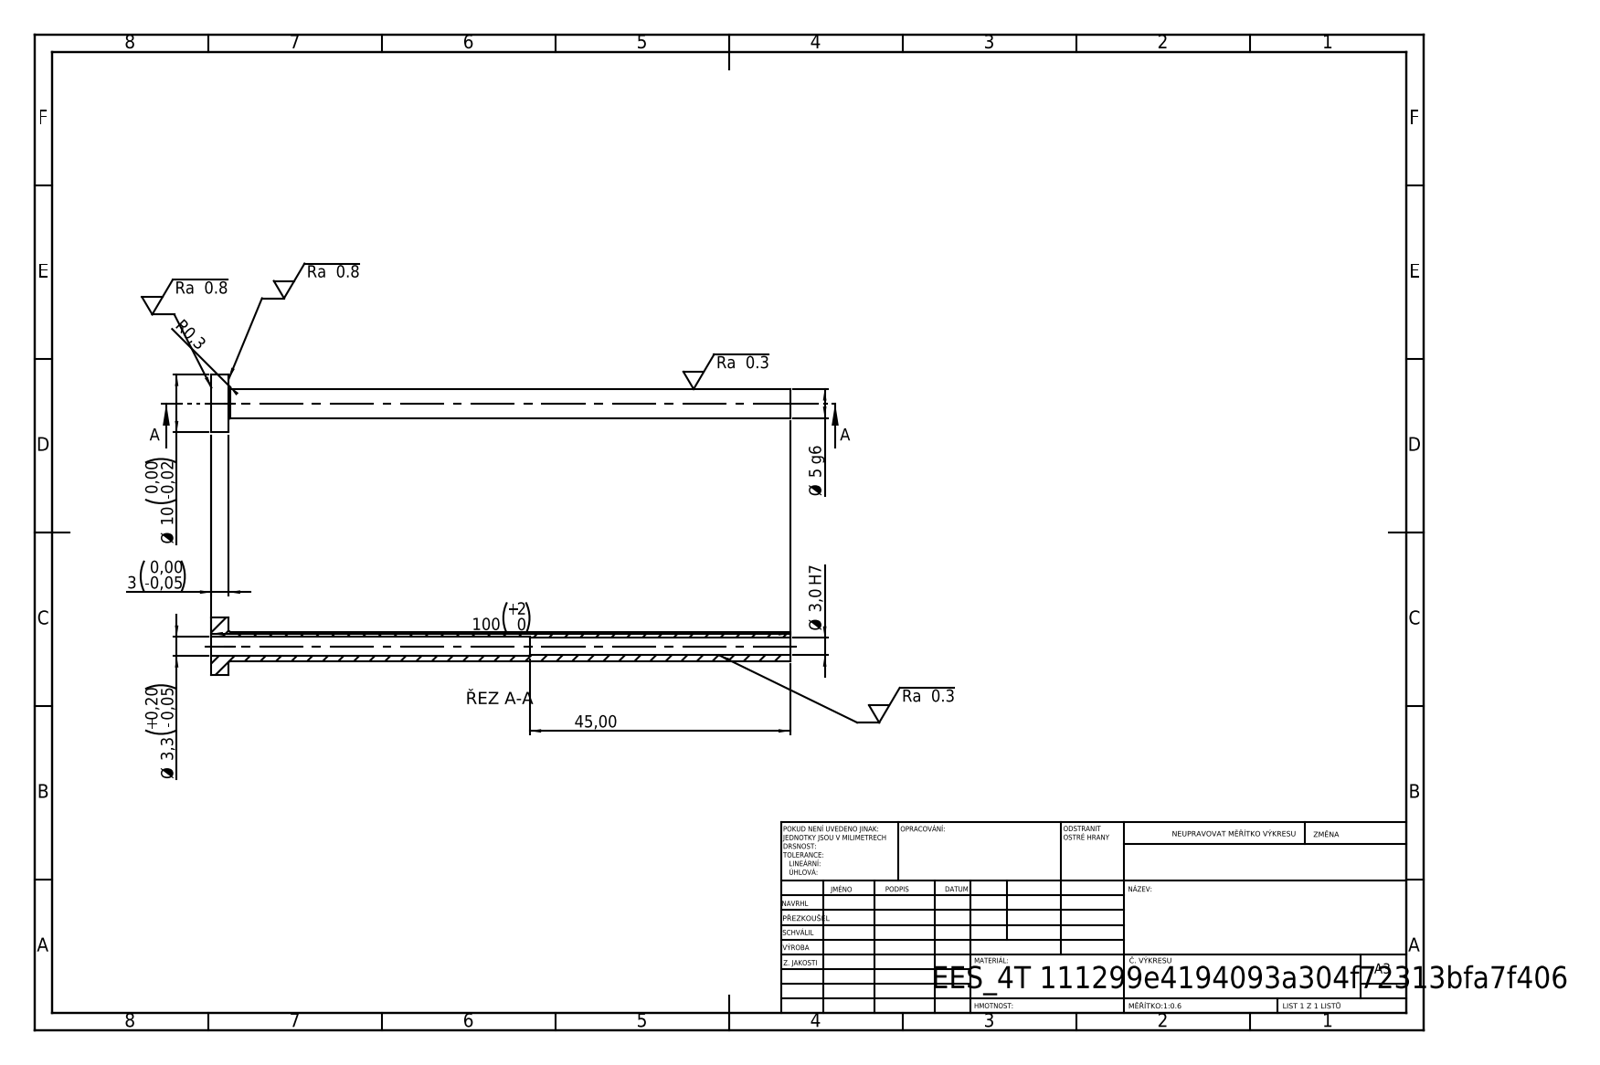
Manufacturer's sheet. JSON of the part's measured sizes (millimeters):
{"step_written_by": "SolidWorks 2019 (CONFIG_CONTROL_DESIGN)", "units": "millimeters", "bodies": {"solids": 1, "faces": 14, "planar": 4, "cylindrical": 8, "other": 2}, "overall_size": [100, 10, 10], "volume_mm3": 1352, "surface_area_mm2": 2753, "round_holes": [[3, 1], [3.3, 1]], "round_bosses_or_shafts": [[10, 1], [5, 1]], "face_to_face_distances": [3, 100, 97, 55, 52, 45]}
